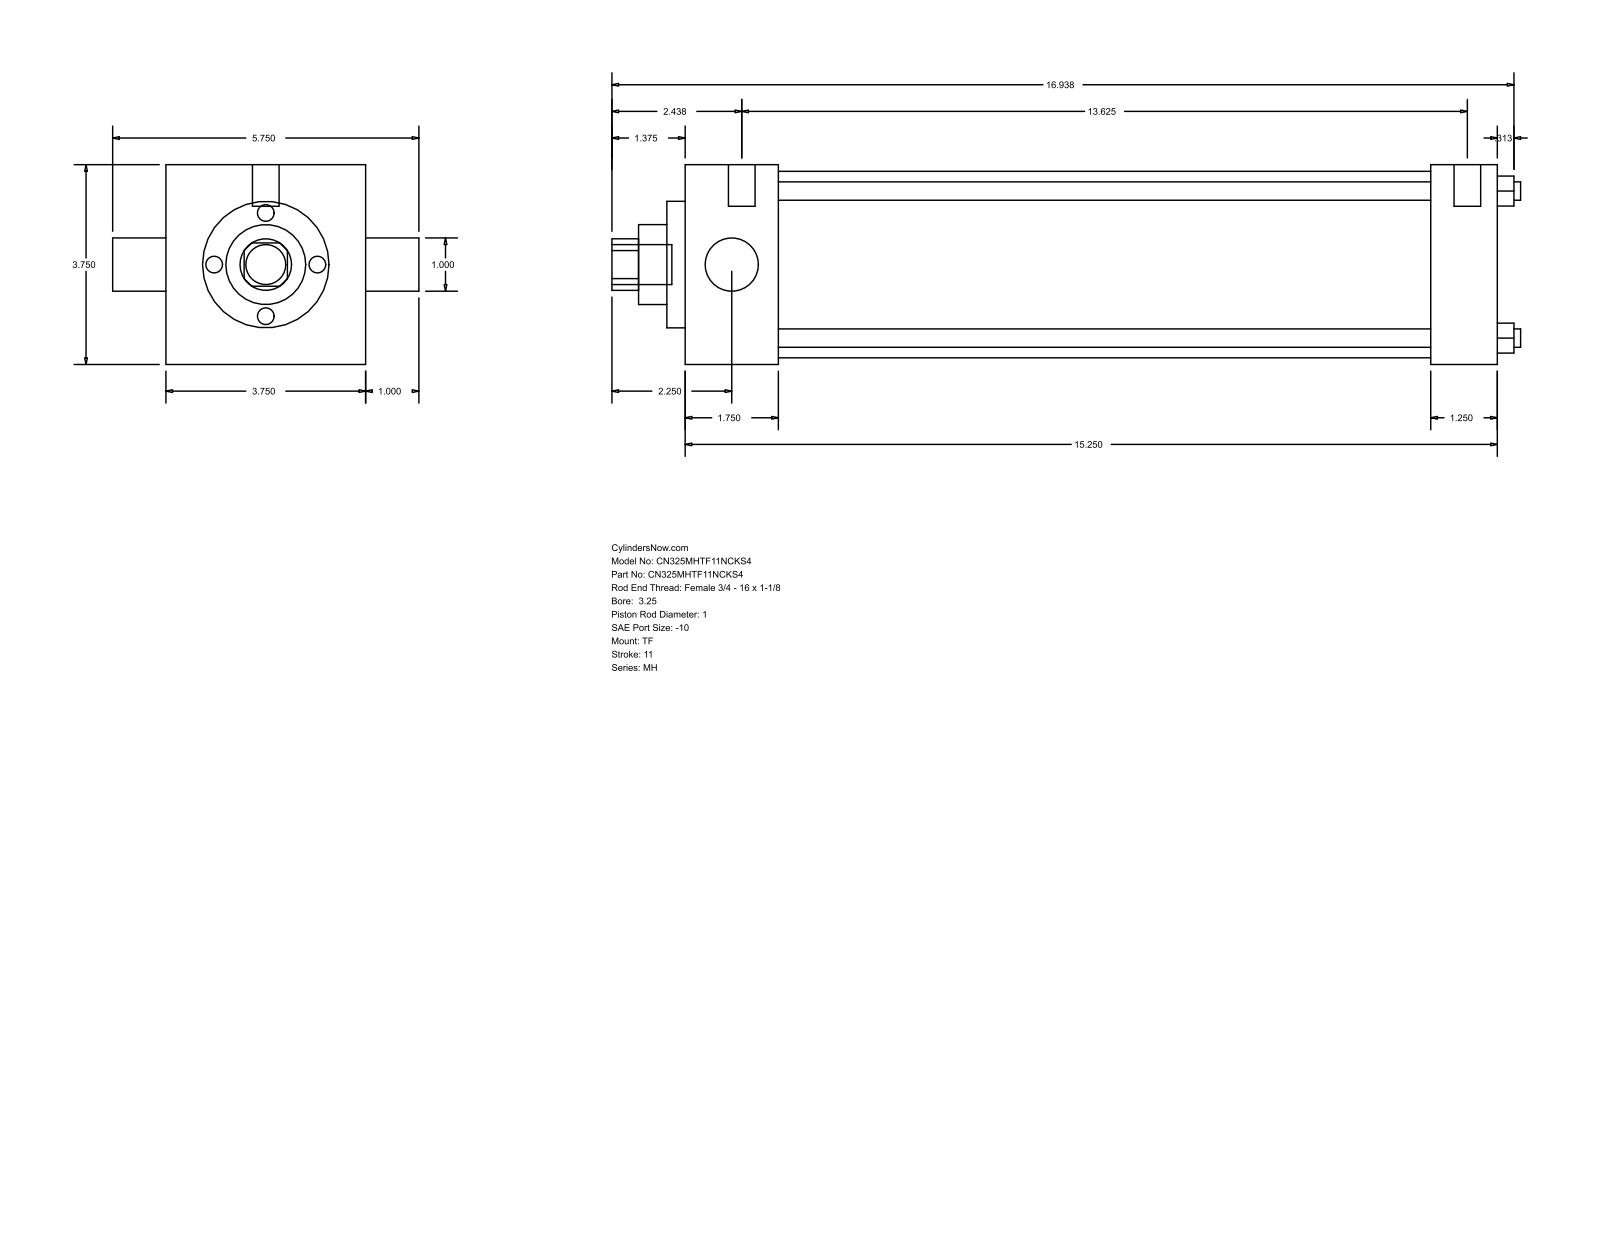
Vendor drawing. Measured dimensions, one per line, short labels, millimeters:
name: MH_TF__0325_1
written by: GSSL Pune (CONFIG_CONTROL_DESIGN)
unit: mm
bodies: 0 solids, 86 faces (61 planar, 25 cylindrical, 0 other)
size: 433.39 × 146.05 × 95.25
holes: 4× ⌀8.76, 2× ⌀25.4, 1× ⌀38.1, 1× ⌀60.33, 1× ⌀88.9
bosses: 3× ⌀5.56, 2× ⌀12.7, 1× ⌀19.05
rounds: 1× R12.29
face distances: 95.24, 387.35, 44.46, 355.6, 311.14, 342.89, 31.75, 8.73, 53.19, 364.33
hole spacings: 49.57, 70.1, 99.14
